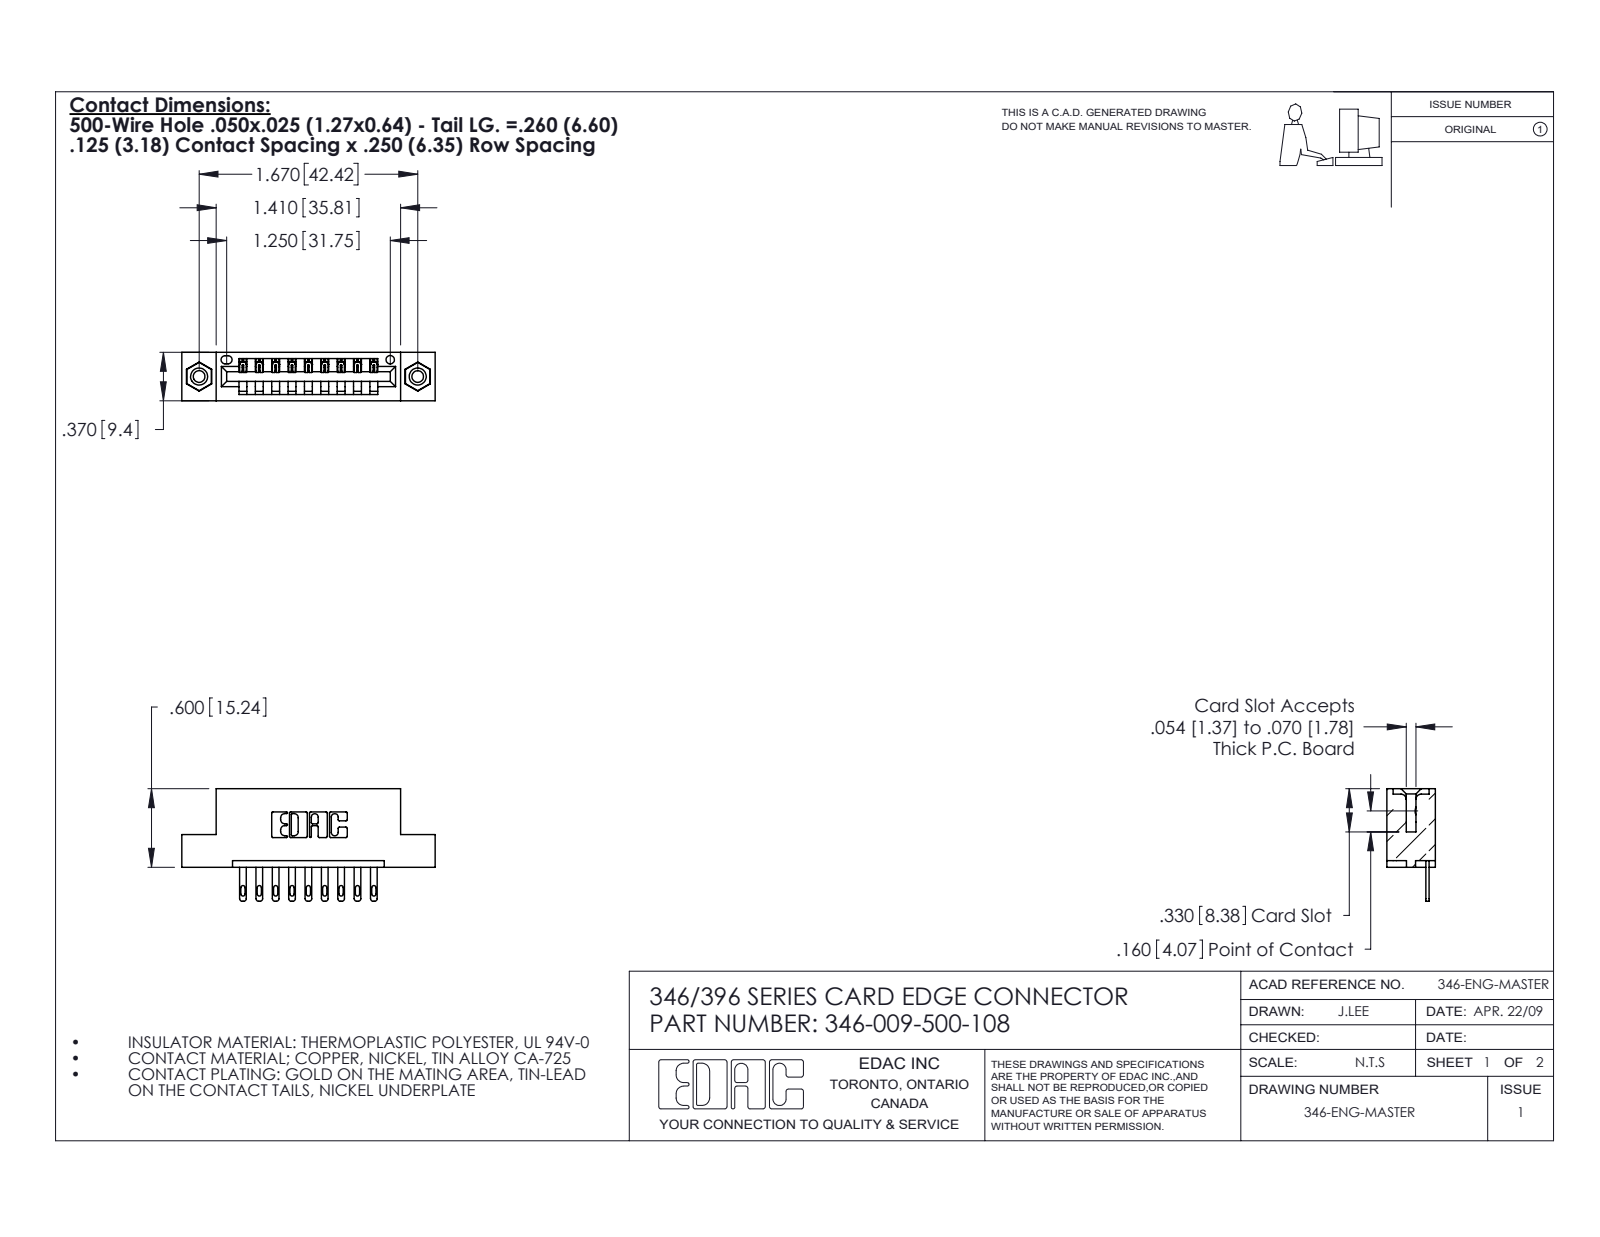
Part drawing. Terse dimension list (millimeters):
name: 346-009-500-108; 345-250-001_345-250-003-102; 345-292-001_345-293-100; 346 Part_Flush Mounting Lugs - 0.156 Dia-TI
written by: SolidWorks 2020 (CONFIG_CONTROL_DESIGN)
unit: mm
bodies: 12 solids, 668 faces (414 planar, 238 cylindrical, 16 other)
size: 49.1 × 21.8 × 9.4
volume: 4 470 mm³; area: 5 281 mm²
holes: 2× ⌀2.3, 2× ⌀3.2, 2× ⌀4, 1× ⌀1.6
bosses: 2× ⌀3.9
rounds: 22× R0.3, 18× R0.2, 18× R0.4, 18× R0.5, 6× R0.2, 6× R0.8, 3× R0.7, 2× R0.8
face distances: 6.4, 1.2, 8.2, 9.4, 1.8, 7.6, 0.6, 3.8, 5.6, 2.5
hole spacings: 6.2, 37.2, 42.4
